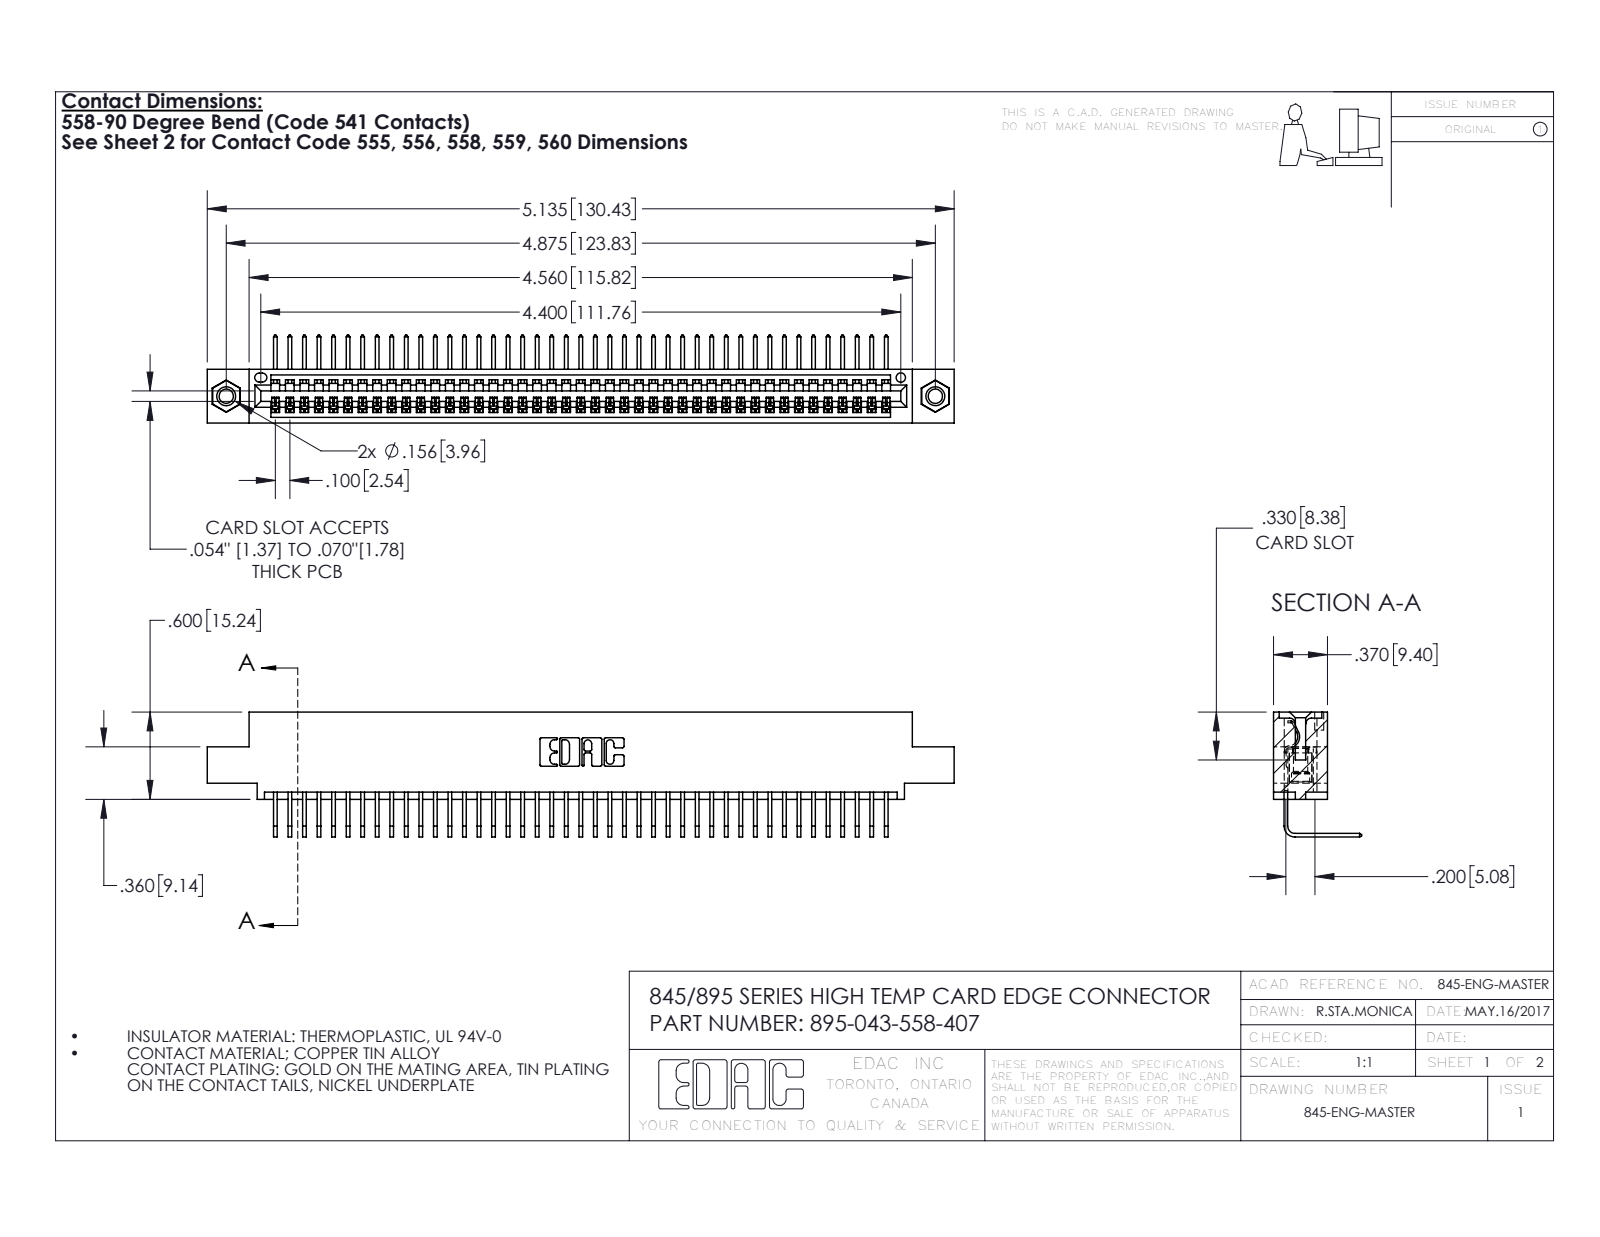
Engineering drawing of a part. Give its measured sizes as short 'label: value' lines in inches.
name: 345-250-001_345-250-005-103; 395-043-558-407; 345-292-001_558 Tail - 2; 345 Part_0.110 Offset - 0.156 Dia-TI
written by: SolidWorks 2016 (CONFIG_CONTROL_DESIGN)
unit: in
bodies: 46 solids, 2770 faces (1922 planar, 832 cylindrical, 16 other)
size: 5.135 × 0.859 × 0.605
volume: 0.76 in³; area: 27.15 in²
holes: 2× ⌀0.098, 2× ⌀0.125, 2× ⌀0.156, 1× ⌀0.064
bosses: 2× ⌀0.155
rounds: 86× R0.006, 22× R0.01, 6× R0.007, 6× R0.031, 3× R0.026, 2× R0.031, 2× R0.04, 1× R0.014
face distances: 0.072, 0.298, 0.37, 0.2, 0.098, 0.272, 0.025, 0.225, 0.149, 0.072
hole spacings: 0.27, 4.639, 4.875
